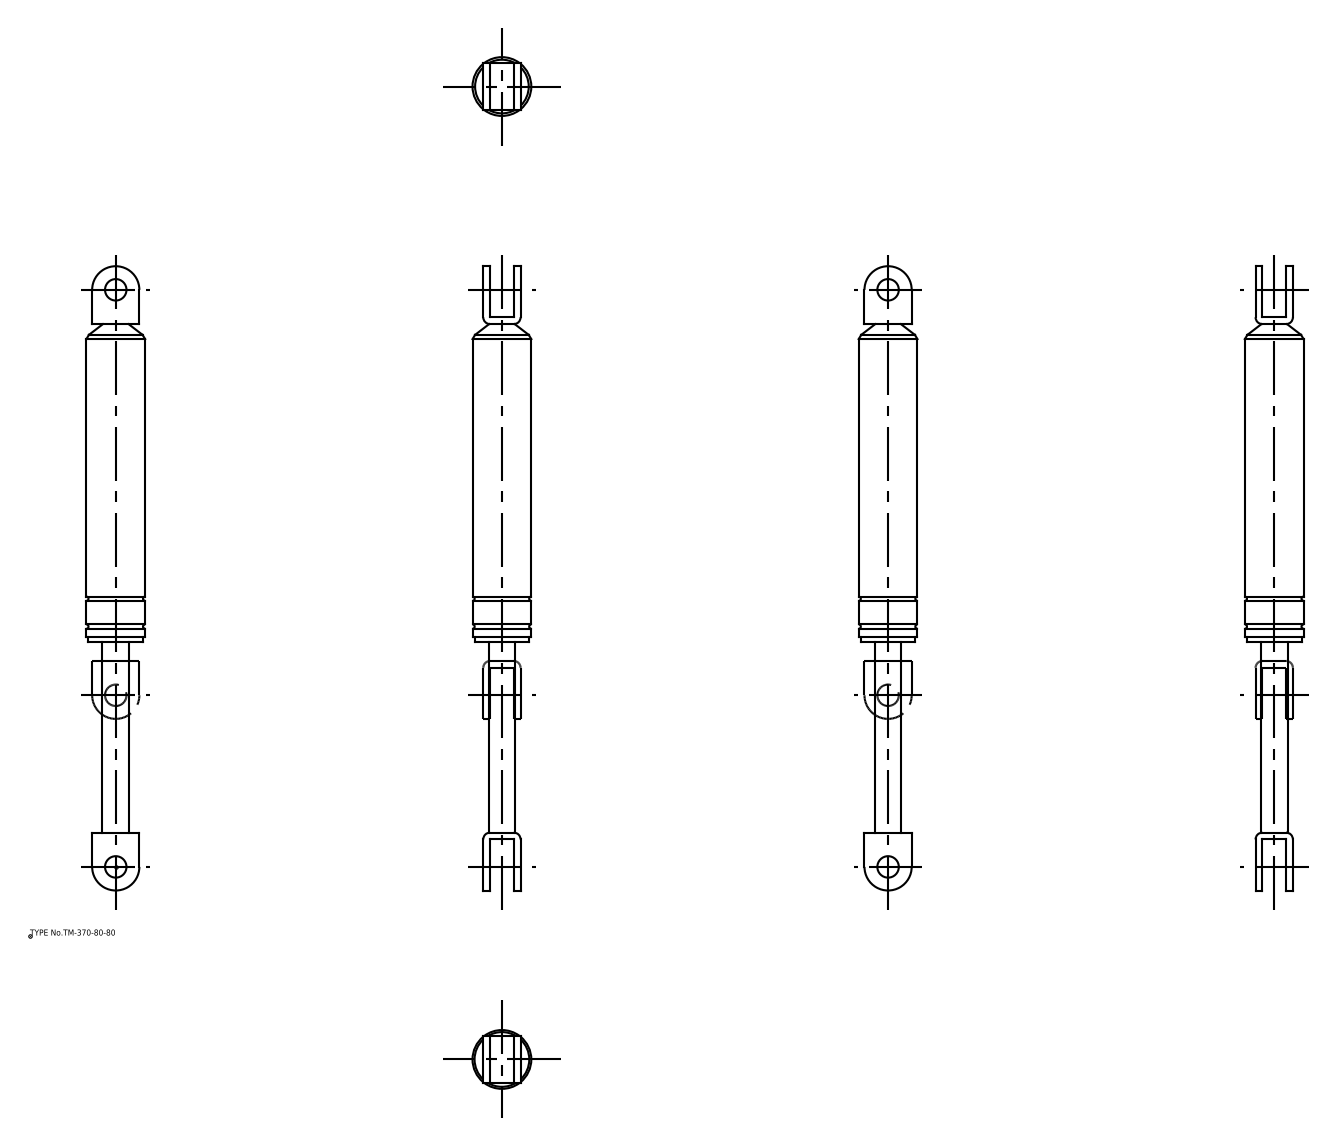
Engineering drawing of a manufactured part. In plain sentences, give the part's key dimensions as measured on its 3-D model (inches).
The part is named "TM_370_80_80; TM_370_80_80_div". Its 3-D file was written by "spGate 16.7.1 (AUTOMOTIVE_DESIGN)". It is 2 solids with 64 faces: 22 planar, 32 cylindrical and 10 other. Overall it measures 11.457 by 1.11 by 1.11 inches. Its volume is 6.339 cubic inches and its surface area 35.67 square inches. Round holes: 2 of diameter 0.394. Round bosses or shafts: 1 of diameter 1.11, 1 of diameter 1.079, 1 of diameter 1.004, 1 of diameter 0.492. Partial cylindrical surfaces (rounded edges, fillets, slot ends): 4 of radius 0.126, 2 of radius 0.433. The main face-to-face distances are 0.126, 0.559, 0.685, 0.433, 0.866, 9.457, 3.63, 9.583, 5.953, 5.827. The hole center spacings are 10.591.
